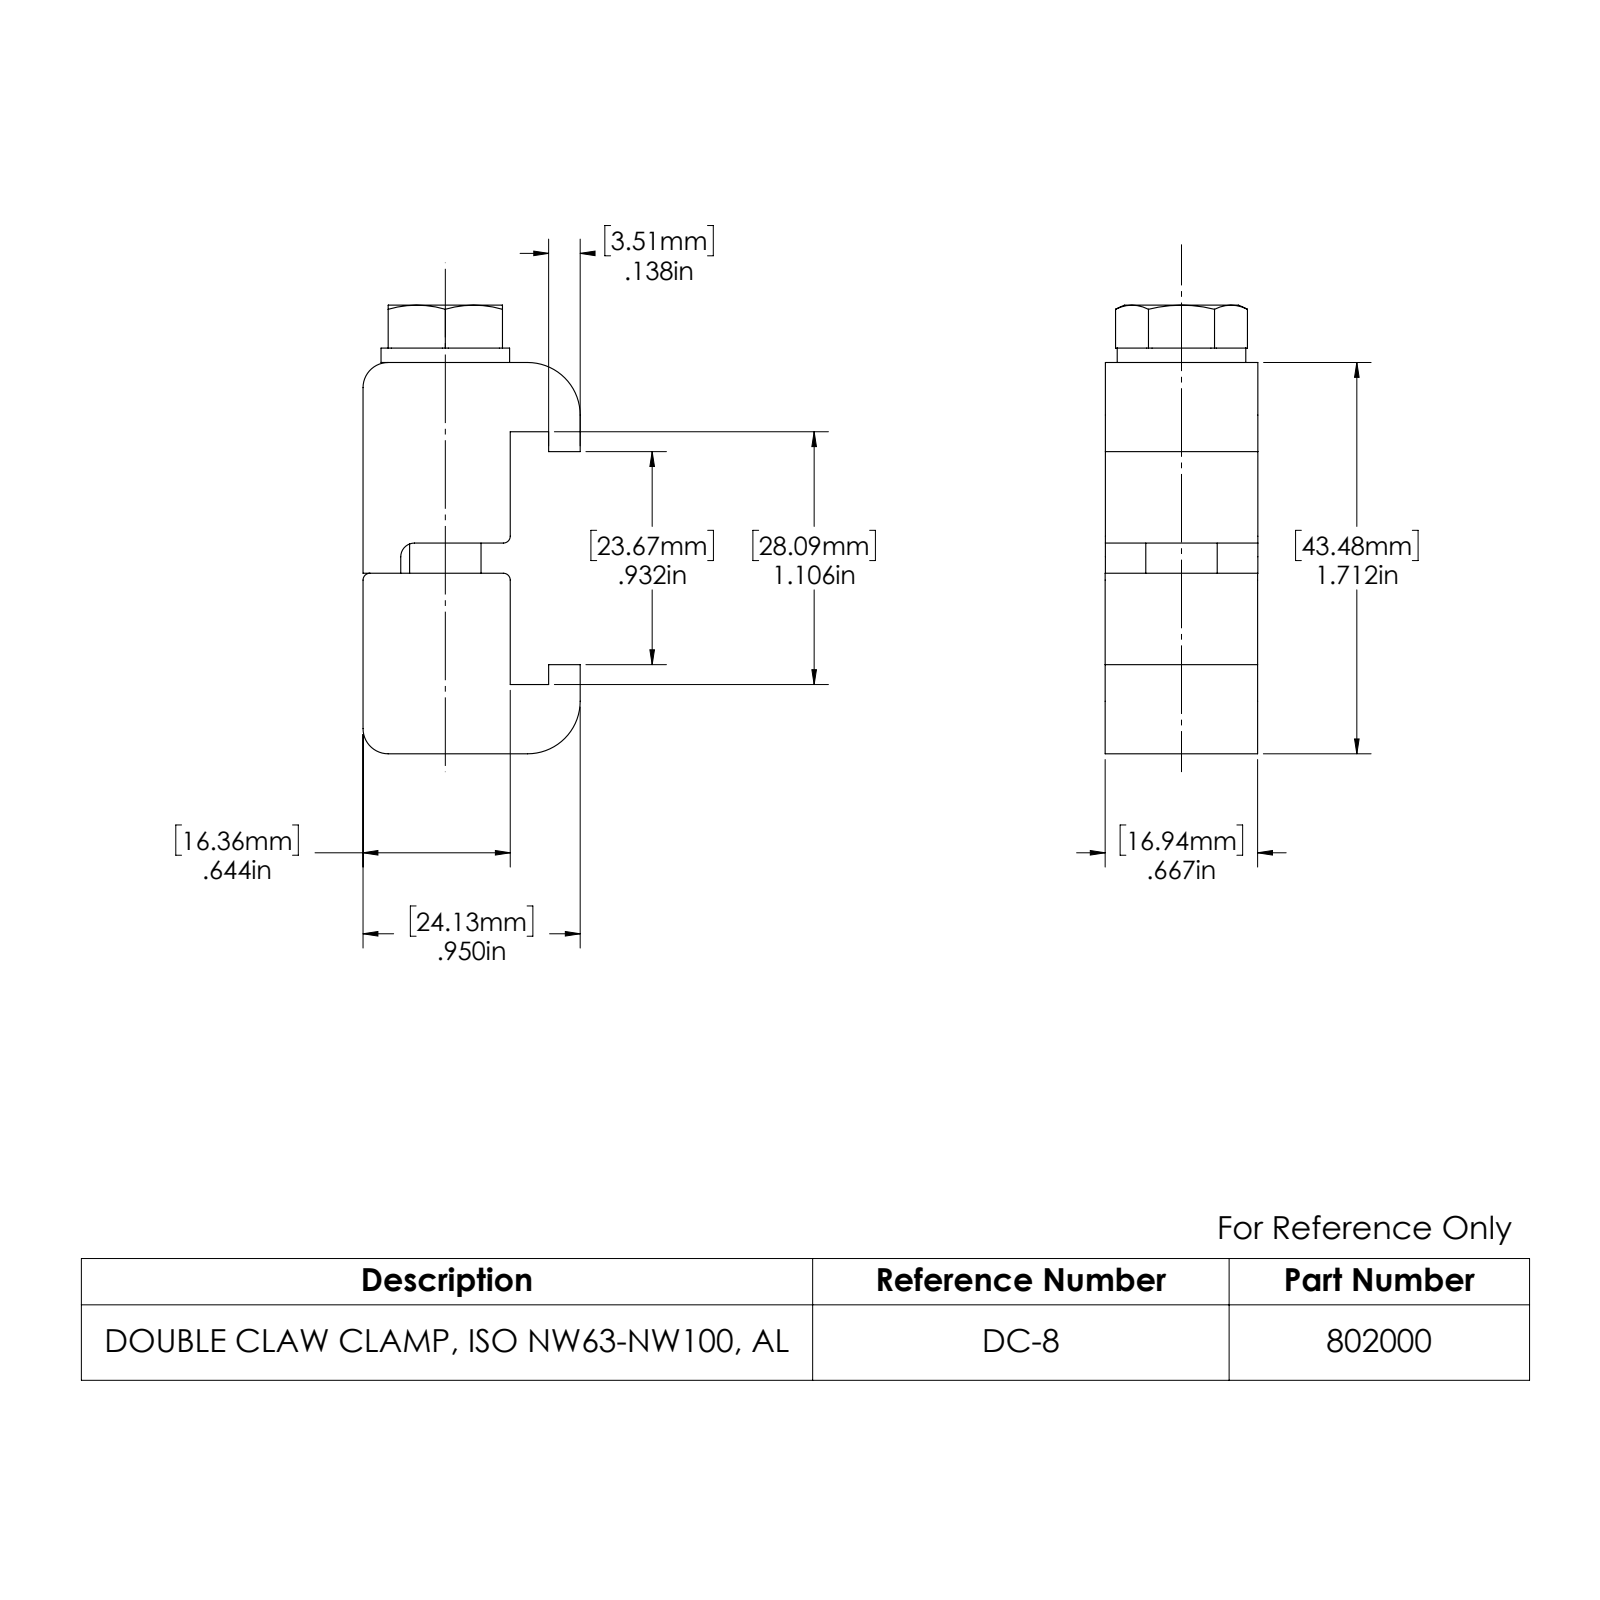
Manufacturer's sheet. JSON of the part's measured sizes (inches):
{"part_name": "802000; SUB; 980230; 980220", "step_written_by": "SolidWorks 2022 (CONFIG_CONTROL_DESIGN)", "units": "inches", "bodies": {"solids": 4, "faces": 55, "planar": 33, "cylindrical": 18, "other": 4}, "overall_size": [1.963, 0.95, 0.668], "volume_in3": 0.888, "surface_area_in2": 11.43, "round_holes": [[0.268, 1], [0.313, 1], [0.33, 1]], "round_bosses_or_shafts": [[0.563, 1]], "partial_cylinders_radius": [[0.03, 3], [0.11, 2], [0.23, 2], [0.06, 1]], "face_to_face_distances": [0.667, 0.922, 0.644, 0.668, 0.666, 0.79, 1.712, 1.775, 0.985, 0.063]}
